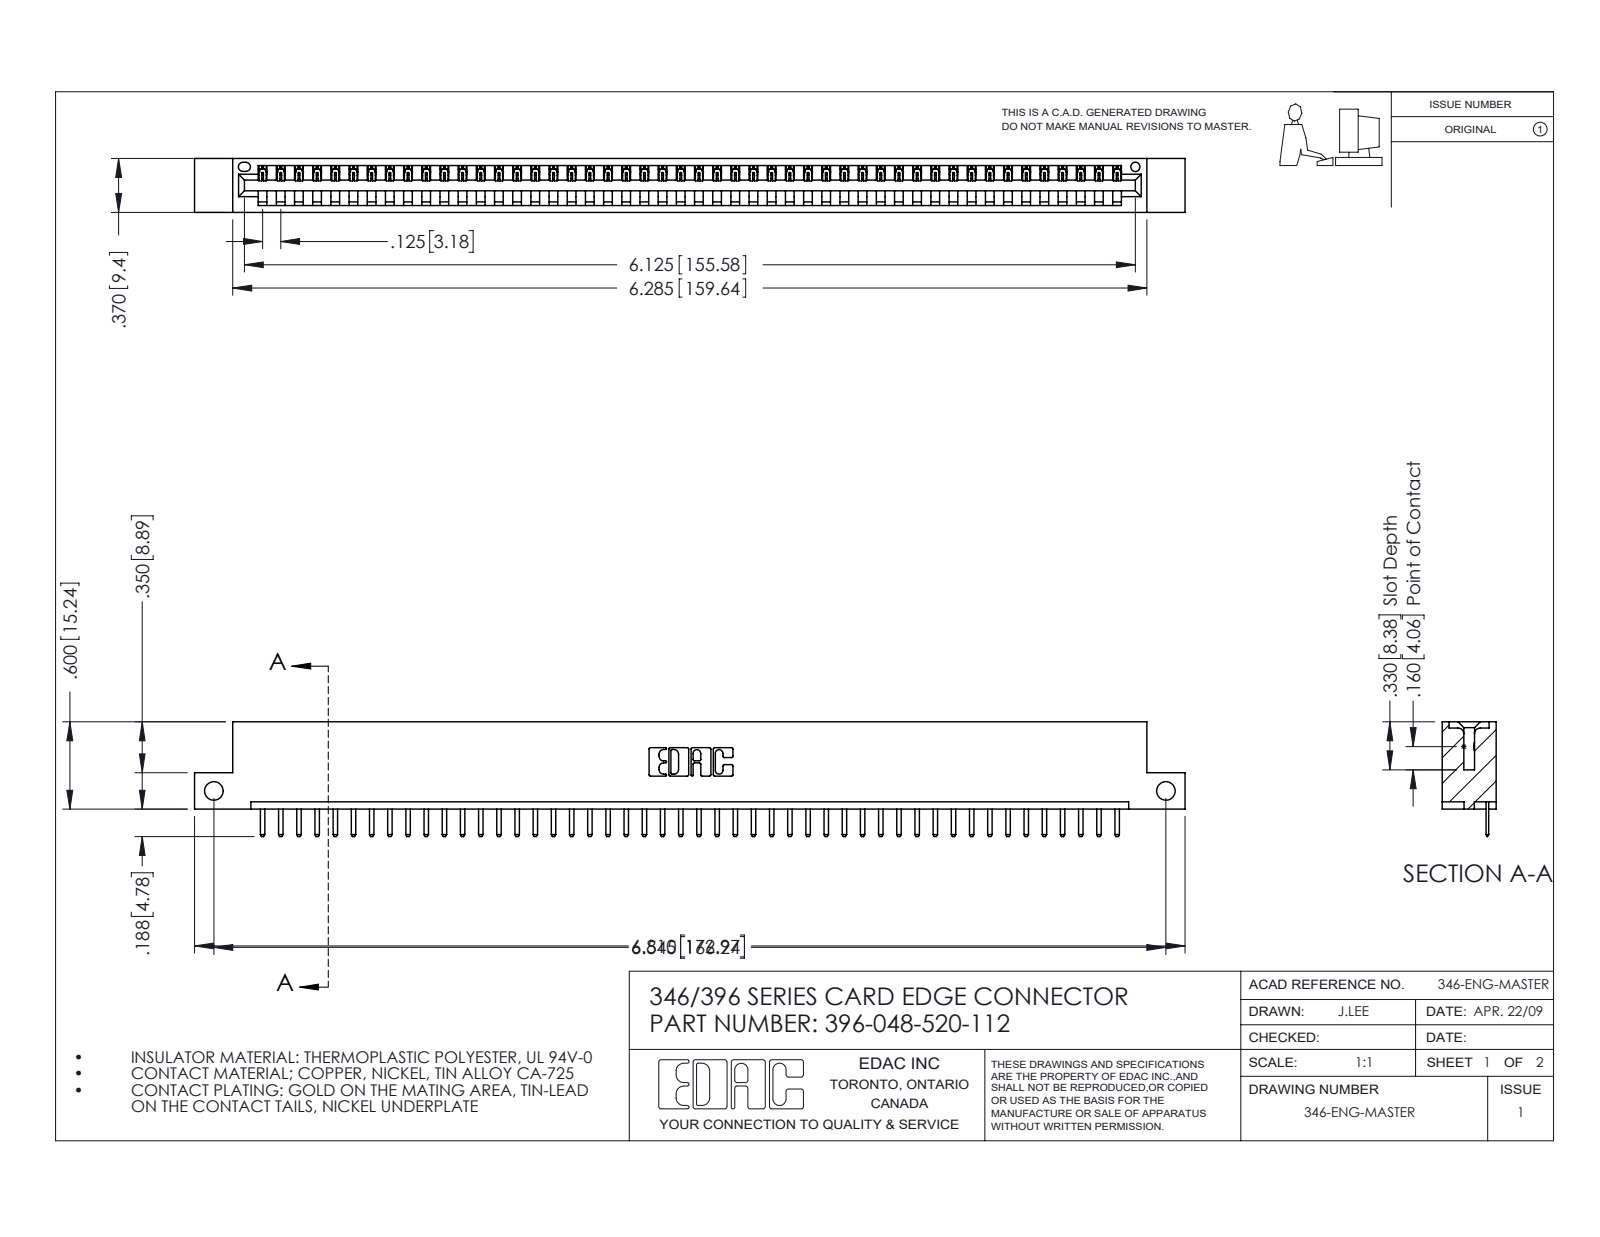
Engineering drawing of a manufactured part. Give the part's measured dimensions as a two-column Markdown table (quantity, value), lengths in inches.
| quantity | value |
| --- | --- |
| part name | 345-292-001_345-293-120; 396-048-520-112; 346 Part_Flush Mounting Lugs - Side Mount |
| STEP written by | SolidWorks 2016 (CONFIG_CONTROL_DESIGN) |
| units | inches |
| bodies | 49 solids, 3098 faces (2092 planar, 1006 cylindrical, 0 other) |
| overall size | 6.81 × 0.788 × 0.37 |
| volume | 0.999 in³ |
| surface area | 30.88 in² |
| round holes (diameter × count) | 0.128 × 2, 0.064 × 1 |
| partial cylindrical surfaces (radius × count) | 0.01 × 98, 0.006 × 96, 0.01 × 22, 0.007 × 6, 0.031 × 6, 0.026 × 3, 0.031 × 2, 0.04 × 2 |
| main face-to-face distances | 0.048, 0.322, 0.37, 0.25, 0.148, 0.222, 0.1, 0.174, 0.072, 0.298 |
| hole center spacings | 6.545 |
